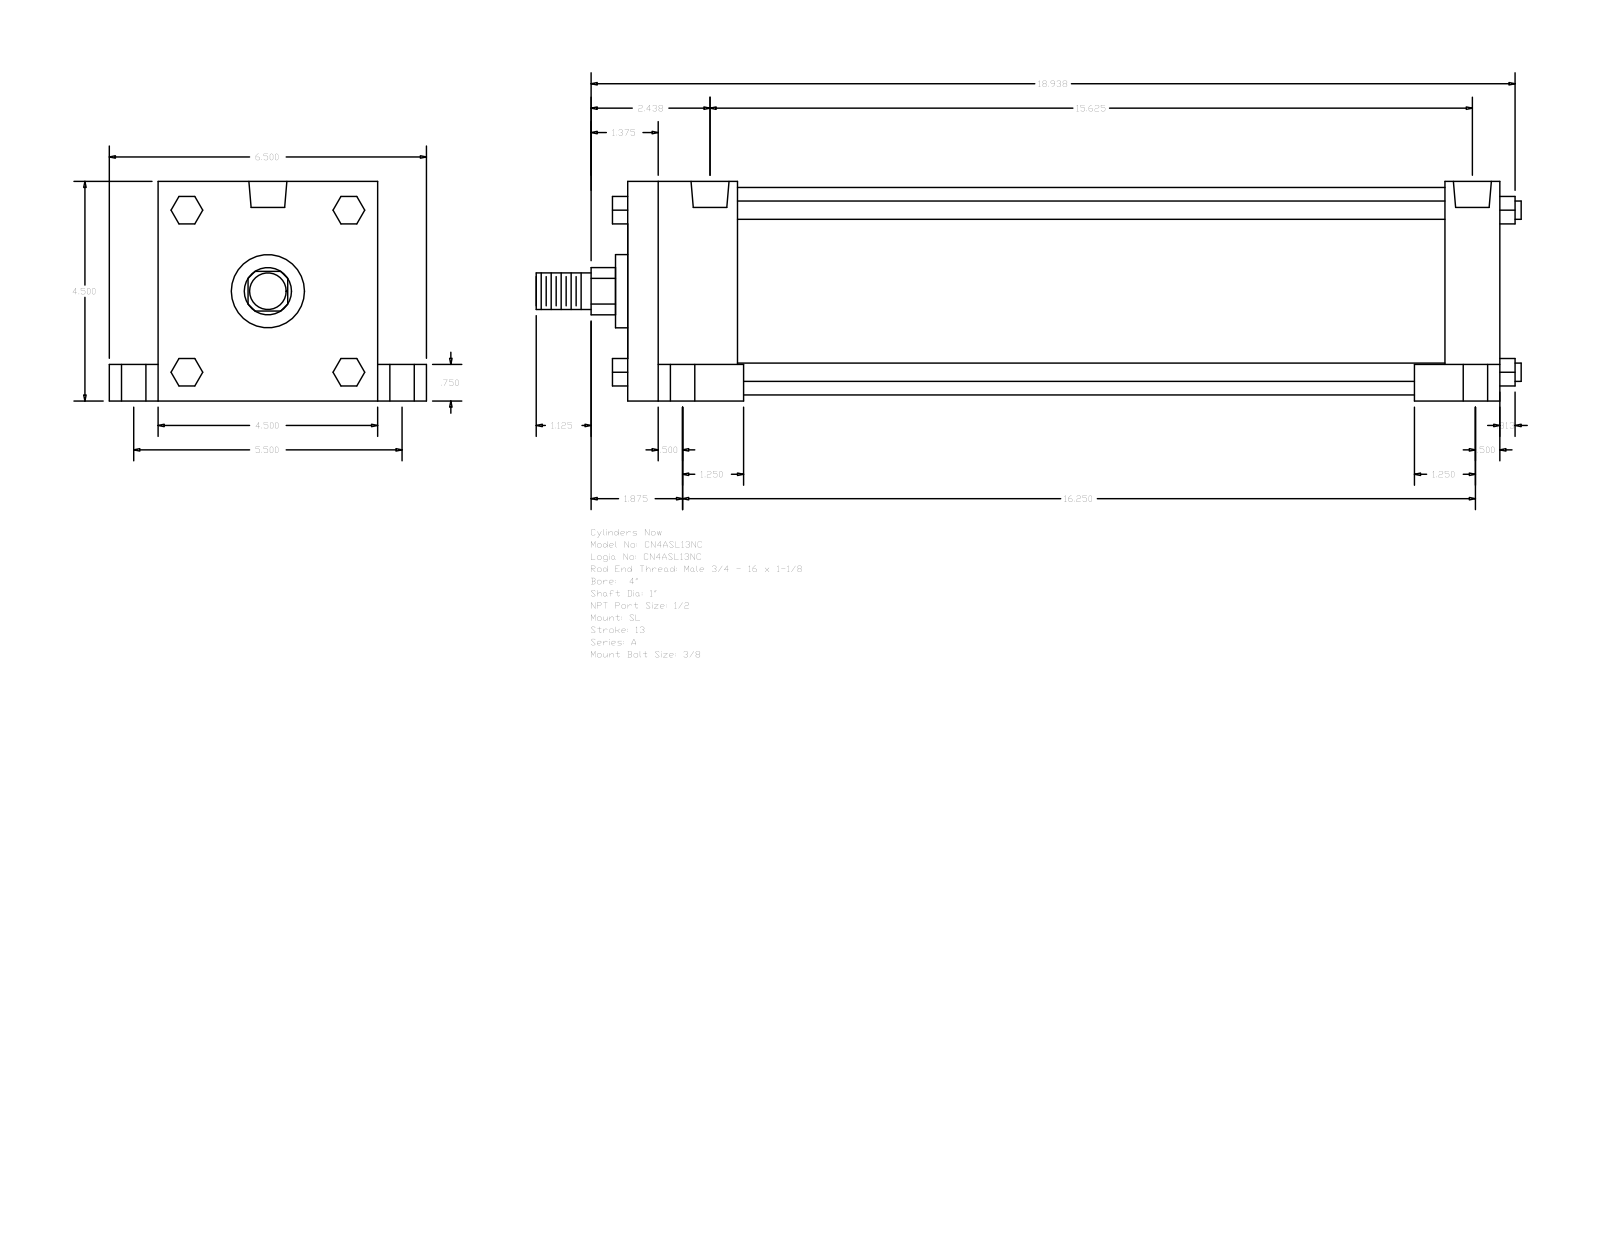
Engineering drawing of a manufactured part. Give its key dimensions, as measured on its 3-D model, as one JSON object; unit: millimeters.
{"part_name": "A_SL__0400_1", "step_written_by": "GSSL Pune (CONFIG_CONTROL_DESIGN)", "units": "millimeters", "bodies": {"solids": 0, "faces": 150, "planar": 114, "cylindrical": 36, "other": 0}, "overall_size": [512.76, 165.1, 114.3], "round_holes": [[8.73, 4], [12.7, 4], [19.05, 4], [19.77, 2]], "round_bosses_or_shafts": [[9.53, 4], [107.95, 1], [38.1, 1], [25.4, 1], [19.05, 1]], "partial_cylinders_radius": [[12.29, 1]], "face_to_face_distances": [114.3, 454.02, 28.57, 57.15, 396.87, 425.45, 368.3, 19.05, 25.4, 139.7], "hole_center_spacings": [3.18, 69.87, 70.01, 71.3, 72, 139.7, 390.52, 393.7]}
